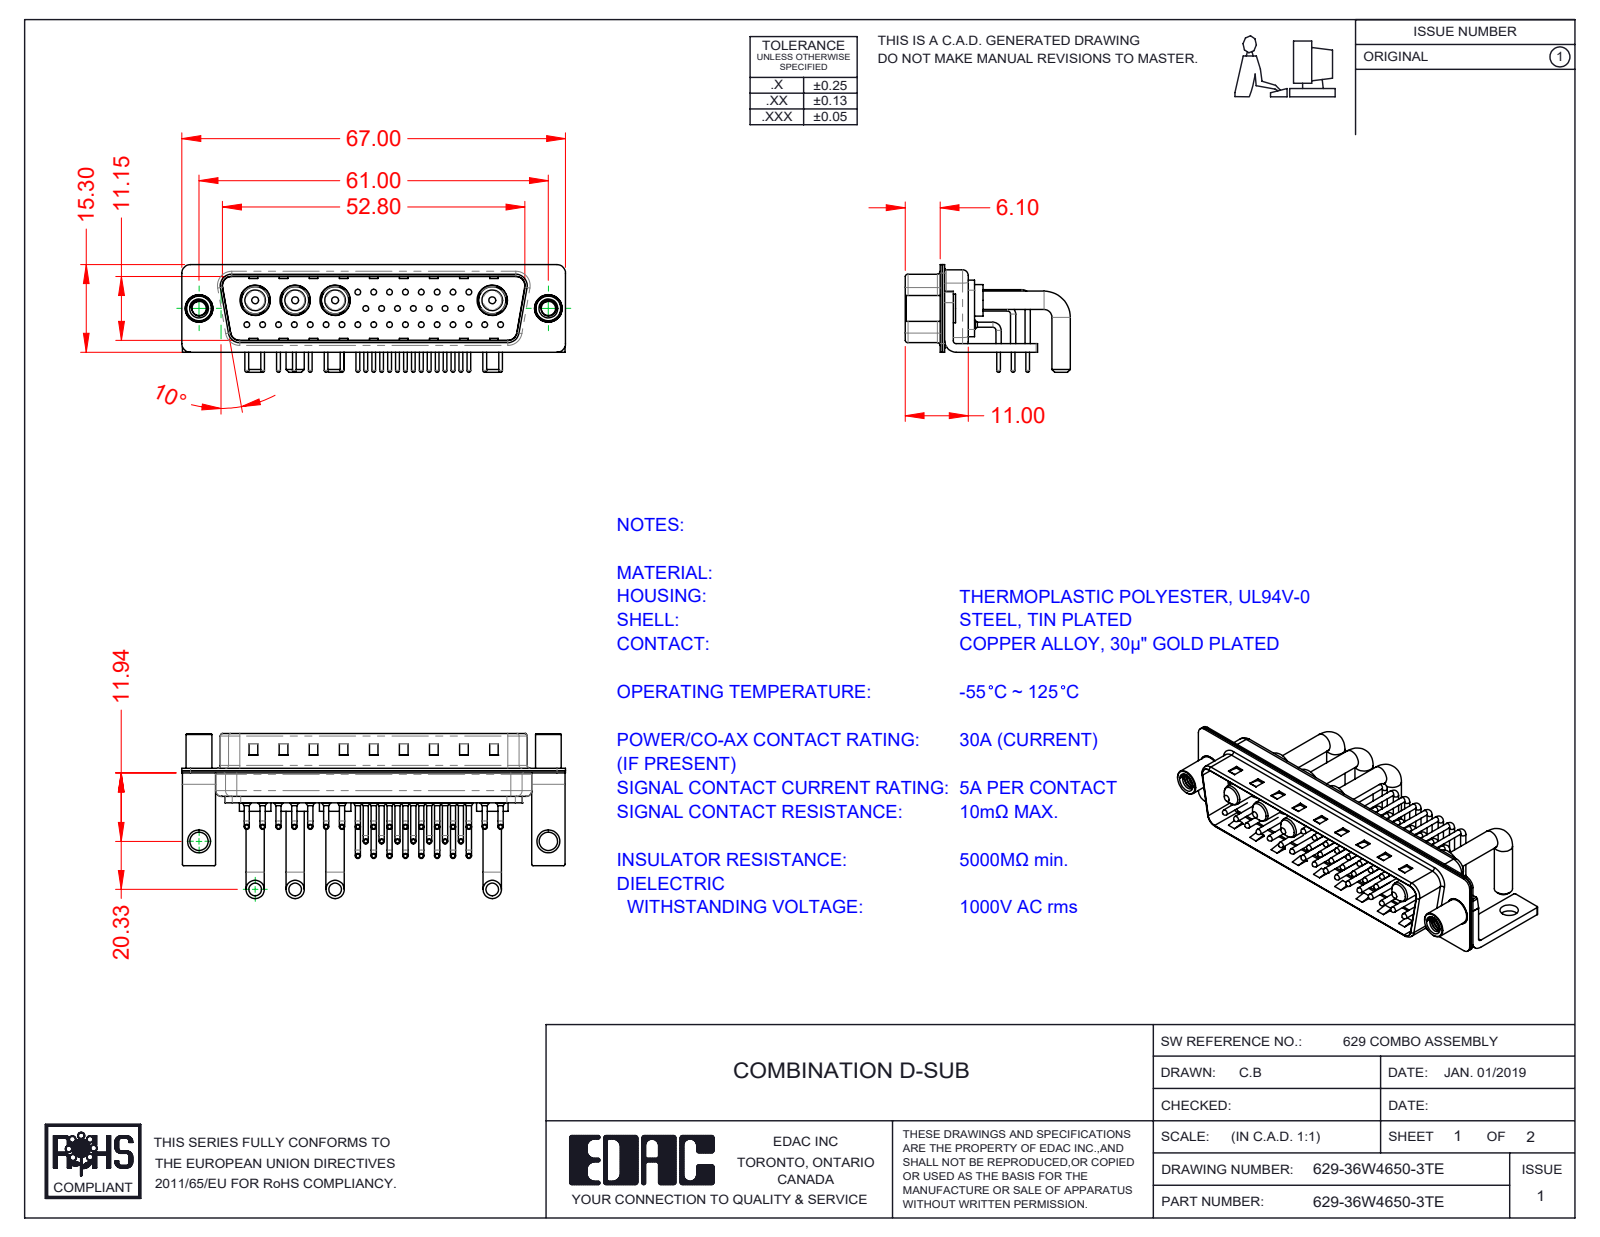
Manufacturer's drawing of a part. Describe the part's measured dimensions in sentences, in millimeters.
The part is named "629Combo Stabilizer Bracket_50 Contacts; 629Combo Contact Row 1_50 Contacts; 629Combo Housing_36W4; 629Combo Shell Rear_50 Contacts (+6 more)". Its 3-D file was written by "SolidWorks 2020 (CONFIG_CONTROL_DESIGN)". It is 47 solids with 4202 faces: 2313 planar, 1449 cylindrical and 440 other. Overall it measures 67 by 28.83 by 18.8 millimeters. Its volume is 6 236 cubic millimeters and its surface area 13 811 square millimeters. Round holes: 32 of diameter 0.75, 32 of diameter 1.6, 32 of diameter 2, 4 of diameter 4.85, 4 of diameter 5.3, 2 of diameter 2.5, 2 of diameter 3.2, 2 of diameter 4, 2 of diameter 4.8. Round bosses or shafts: 64 of diameter 0.9, 32 of diameter 1.5, 32 of diameter 1, 32 of diameter 0.65, 8 of diameter 3.2, 4 of diameter 5.5, 4 of diameter 5.2, 4 of diameter 4.75. Partial cylindrical surfaces (rounded edges, fillets, slot ends): 32 of radius 1.01, 16 of radius 0.25, 16 of radius 1.5, 13 of radius 2, 9 of radius 0.5, 8 of radius 1.6, 4 of radius 0.6, 4 of radius 0.65. The main face-to-face distances are 0.4, 1.5, 11.55, 5.6, 5.2, 0.8, 6, 0.78, 1.9, 1.1. The hole center spacings are 2.77, 5.54, 3.16, 8.31, 11.08, 13.85, 16.62, 19.39.
